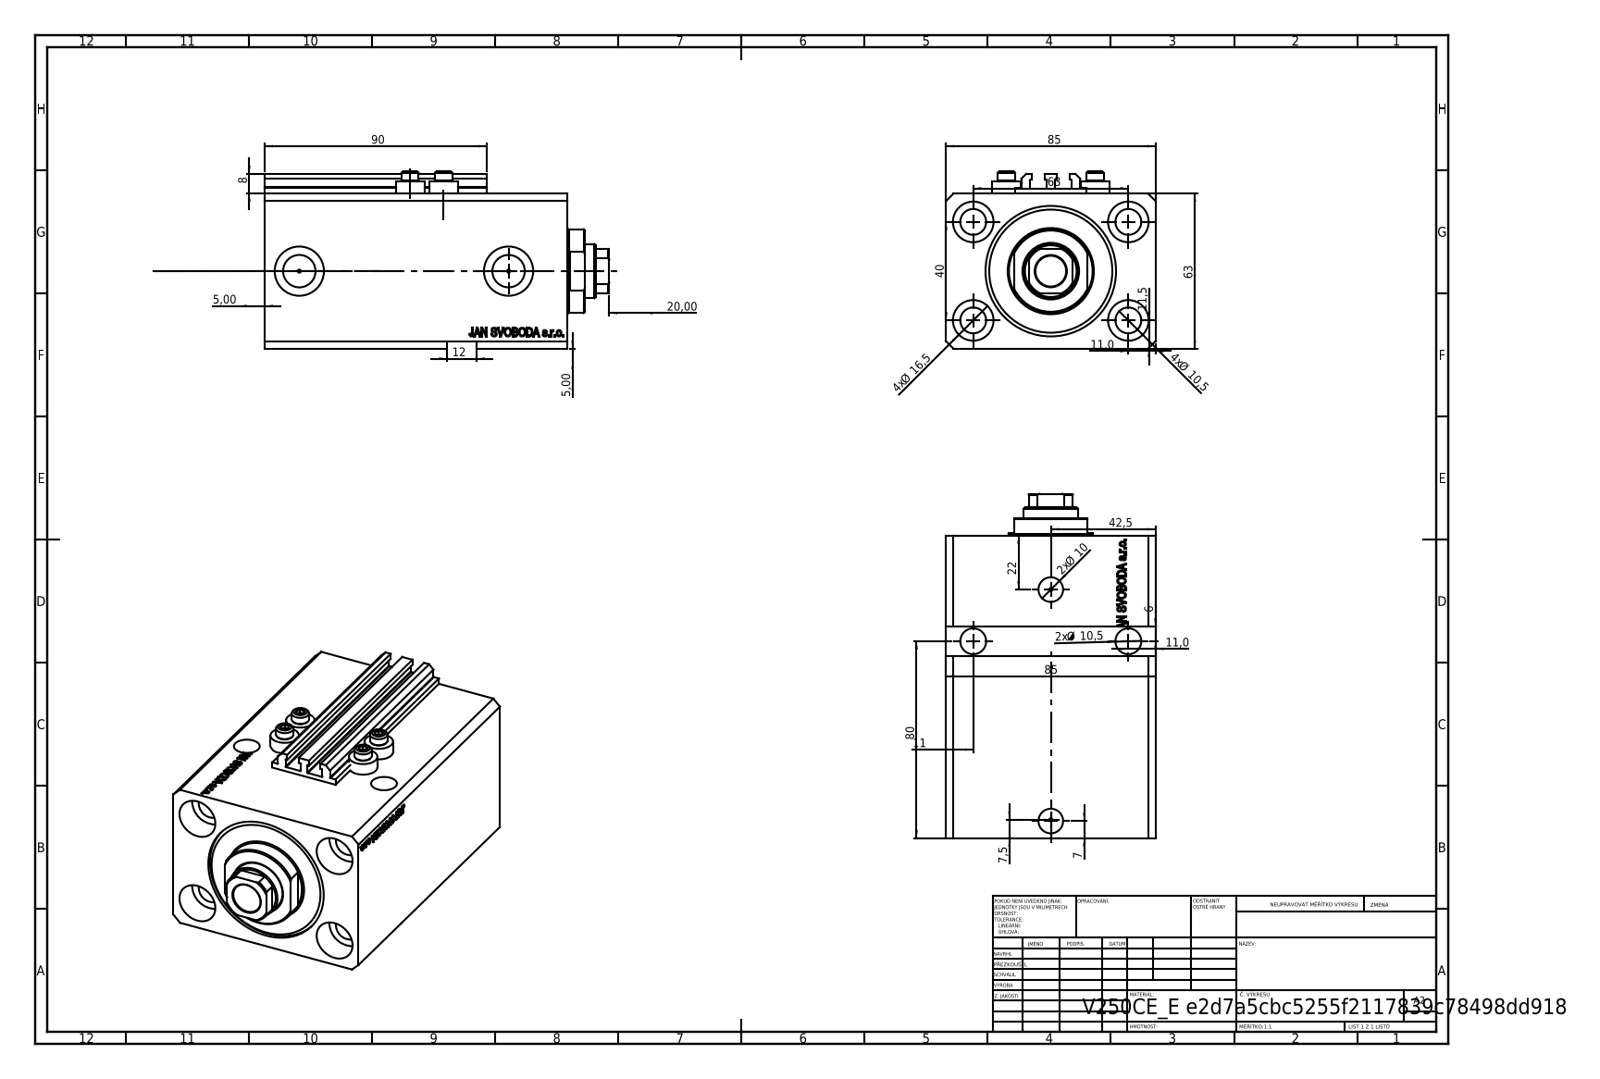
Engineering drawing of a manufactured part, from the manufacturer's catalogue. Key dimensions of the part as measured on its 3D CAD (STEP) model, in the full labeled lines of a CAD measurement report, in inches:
Part name (STEP PRODUCT): V250CE_C_VCP; V250CE_VC_E; V250CE_E_Body; ALLEN BOLT V250CE
STEP written by: SolidWorks 2019 (CONFIG_CONTROL_DESIGN)
Units: inches
Bodies: 8 solids, 1087 faces (535 planar, 126 cylindrical, 426 other)
Overall size (bounding box): 5.508 × 3.346 × 2.835
Volume: 34.44 in³ · Surface area: 185.1 in²
Round holes (diameter × count): ⌀0.413 ×6, ⌀0.049 ×4, ⌀0.157 ×4, ⌀0.65 ×4, ⌀0.394 ×2, ⌀0.518 ×2, ⌀0.787 ×2, ⌀0.492 ×1, ⌀0.866 ×1, ⌀1.575 ×1, ⌀2.087 ×1
Round bosses / shafts (diameter × count): ⌀0.457 ×4, ⌀0.276 ×4, ⌀1.339 ×1
Partial cylindrical surfaces — rounded edges, fillets, slot ends (radius × count): R0.008 ×10, R0.413 ×1
Main face-to-face distances: 2.48, 3.346, 4.843, 3.776, 1.067, 0.449, 3.327, 4.394, 0.118, 2.559
Hole centre spacings: 1.469, 2.48, 0.535, 0.606, 0.983, 1.324, 1.417, 1.491
